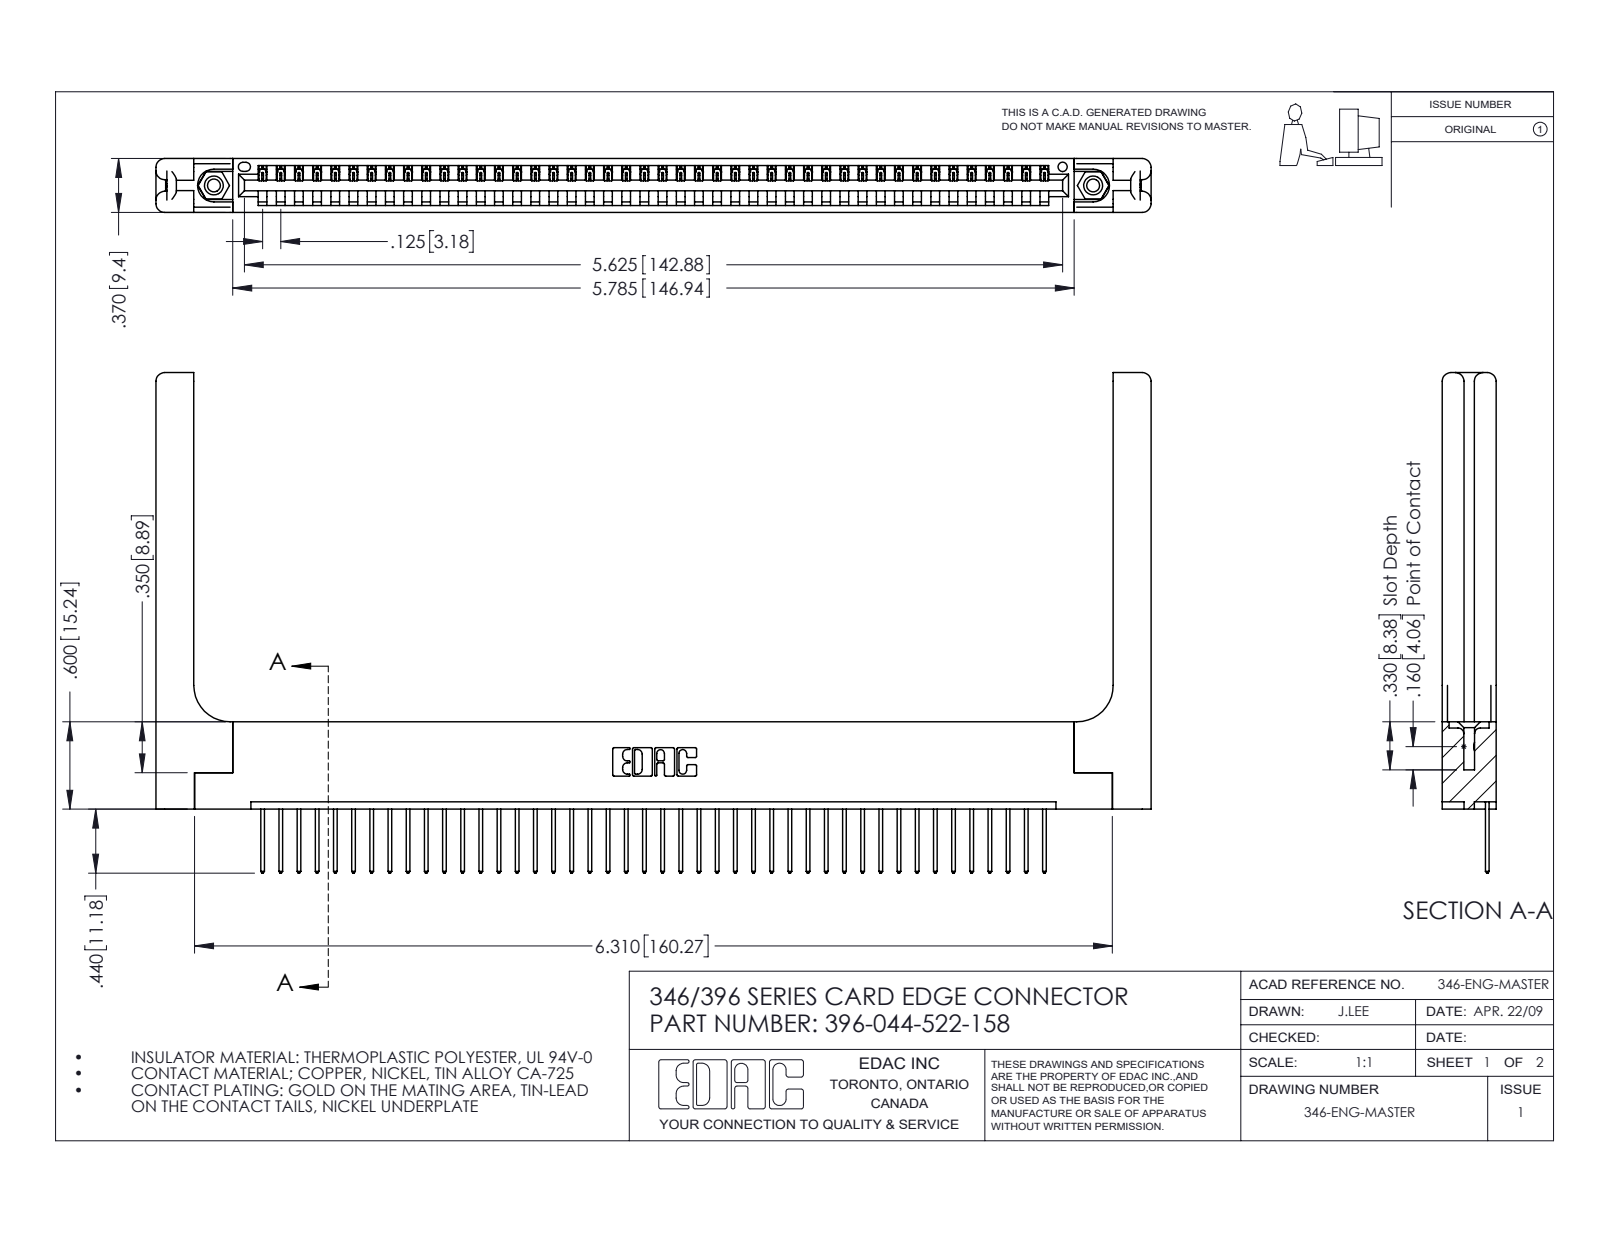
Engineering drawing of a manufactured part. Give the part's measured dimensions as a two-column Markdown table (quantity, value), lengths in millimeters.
| quantity | value |
| --- | --- |
| part name | 346 Part_Flush Mounting Lugs - 0.156 Dia-TH; 345-292-001_345-293-122; 345-250-001_345-250-001-102; 346-220-058_345-220-058 (+1 more) |
| STEP written by | SolidWorks 2016 (CONFIG_CONTROL_DESIGN) |
| units | millimeters |
| bodies | 49 solids, 2930 faces (1984 planar, 886 cylindrical, 60 other) |
| overall size | 173.8 × 87.4 × 9.4 |
| volume | 24 170 mm³ |
| surface area | 26 170 mm² |
| round holes (diameter × count) | 2.3 × 2, 3.2 × 2, 4 × 2, 1.6 × 1 |
| round bosses / shafts (diameter × count) | 3.9 × 2 |
| partial cylindrical surfaces (radius × count) | 0.2 × 88, 0.3 × 88, 0.3 × 22, 1.5 × 16, 0.2 × 6, 0.8 × 6, 0.7 × 3, 0.8 × 2 |
| main face-to-face distances | 9.4, 1.2, 8.2, 1.8, 3.8, 3.8, 6.4, 7.6, 0.6, 5.6 |
| hole center spacings | 6.2, 148.2, 153.5 |
